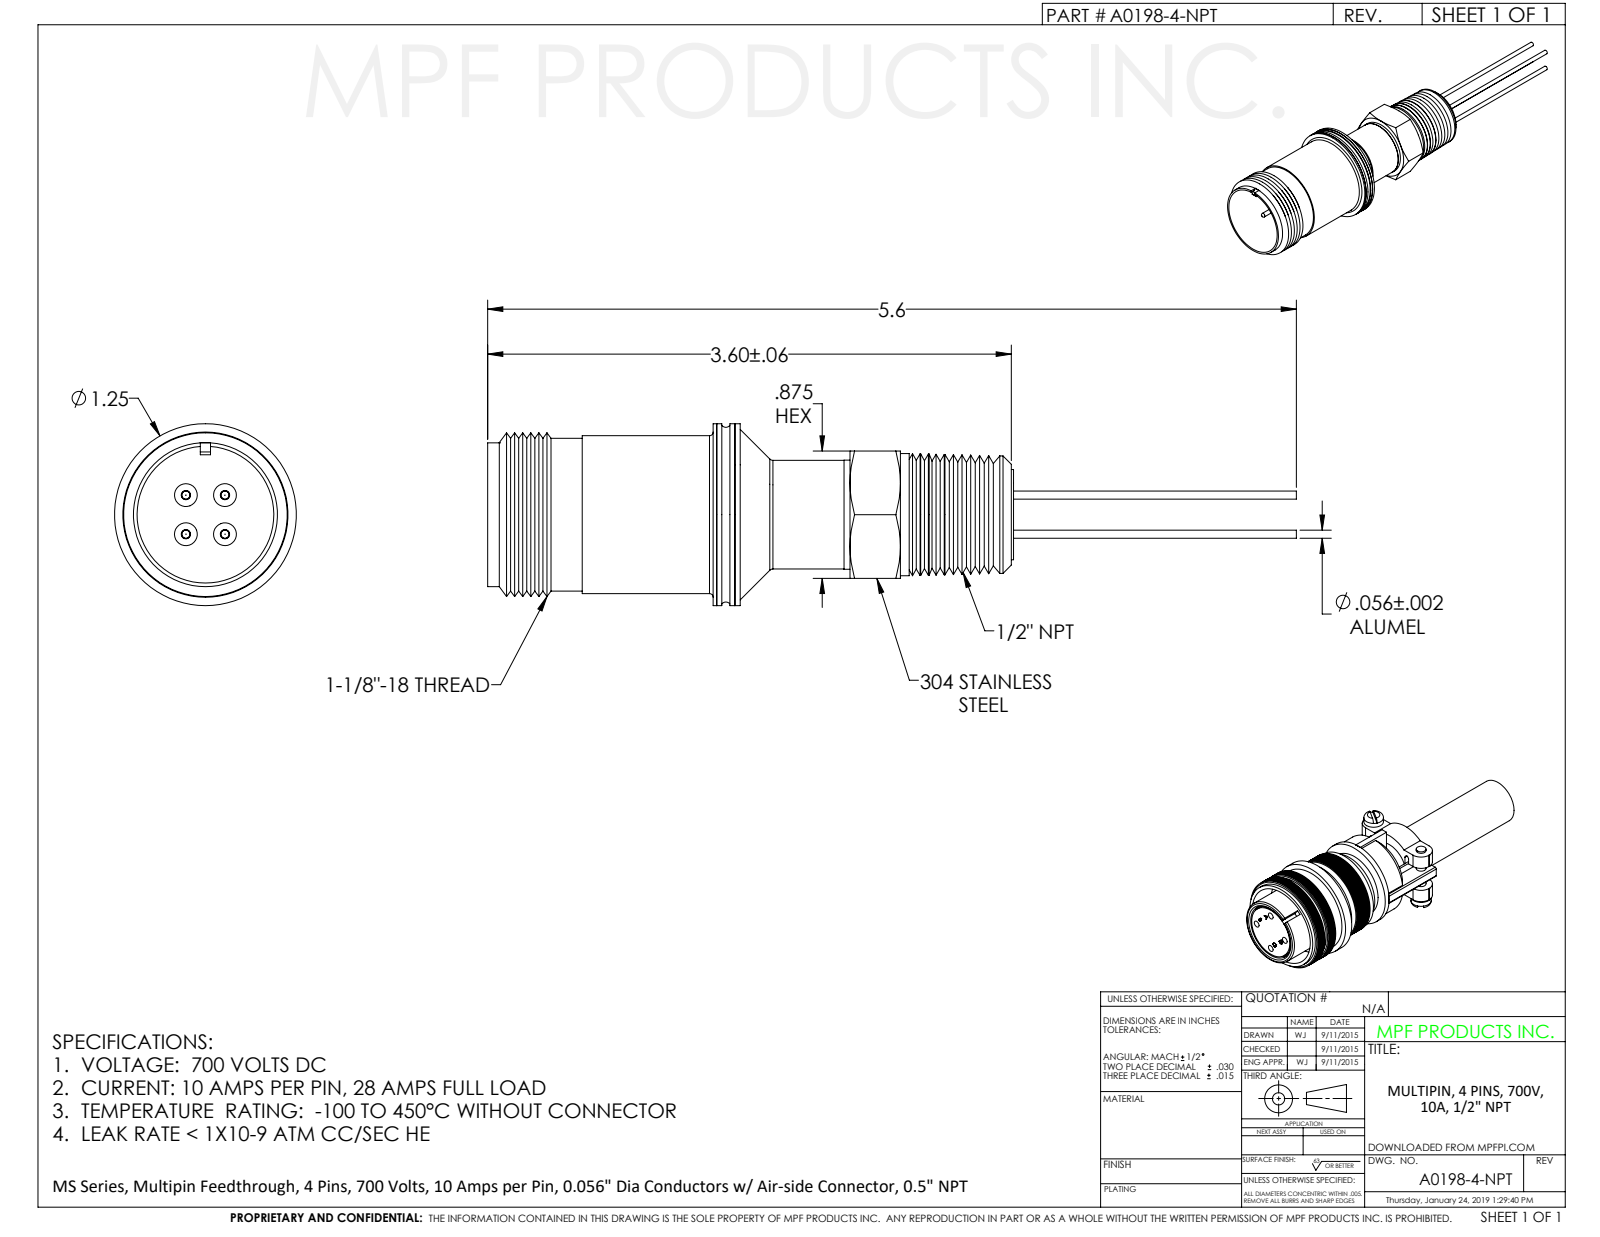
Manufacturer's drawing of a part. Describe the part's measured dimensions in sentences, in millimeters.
The part is named "A0198-4-NPT". Its 3-D file was written by "SolidWorks 2012 (CONFIG_CONTROL_DESIGN)". It is 1 solid with 268 faces: 61 planar, 94 cylindrical and 113 other. Overall it measures 142.1 by 31.8 by 31.8 millimeters. Its volume is 14 300 cubic millimeters and its surface area 22 320 square millimeters. Round holes: 1 of diameter 15.9, 1 of diameter 17.1, 1 of diameter 23.9, 1 of diameter 24.4, 1 of diameter 24.6, 1 of diameter 26.3. Round bosses or shafts: 4 of diameter 4.7, 4 of diameter 4.2, 4 of diameter 1.4, 1 of diameter 31.8, 1 of diameter 27.6, 1 of diameter 26.7, 1 of diameter 25.9, 1 of diameter 25.4. The main face-to-face distances are 1.3, 1, 23.6, 22.2, 3.8, 24.6, 80.8, 82.1, 22.6, 79.8.
